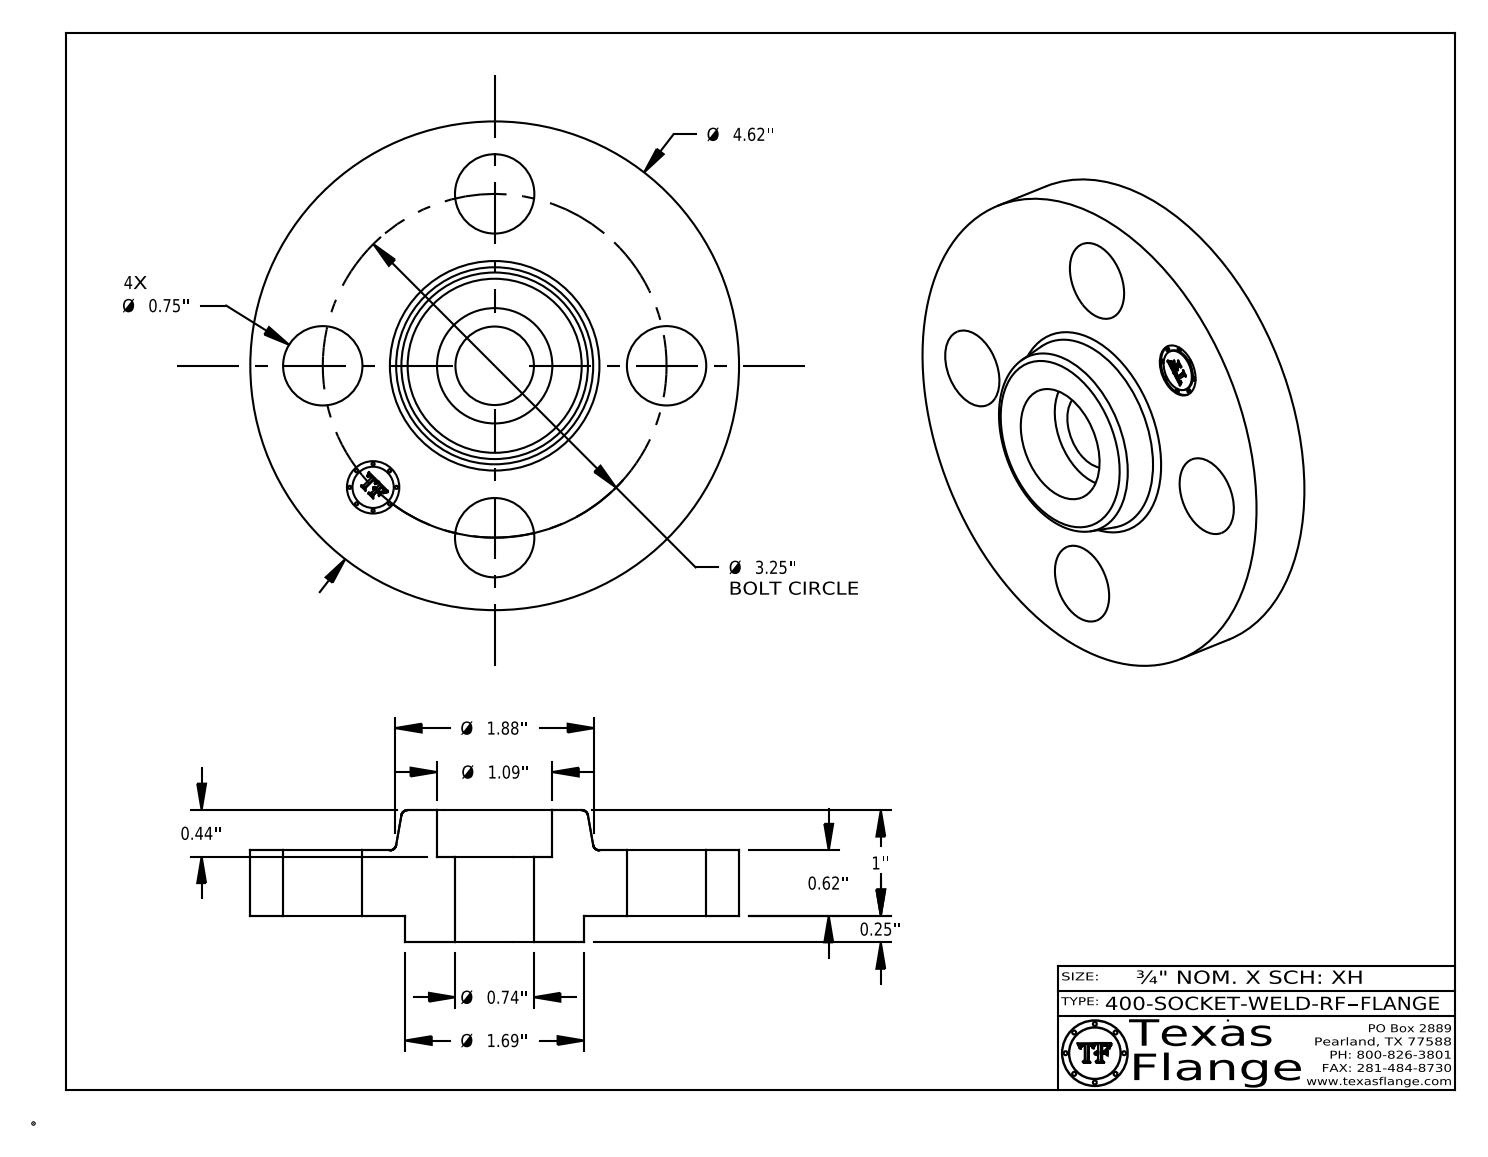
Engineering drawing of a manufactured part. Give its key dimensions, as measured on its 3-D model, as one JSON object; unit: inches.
{"part_name": "400-SOCKET-WELD-RF", "step_written_by": "CATIA V5 STEP AP214 (AUTOMOTIVE_DESIGN)", "units": "inches", "bodies": {"solids": 1, "faces": 412, "planar": 370, "cylindrical": 36, "other": 6}, "overall_size": [4.62, 4.62, 1.25], "volume_in3": 10.08, "surface_area_in2": 50.41, "round_holes": [[0.75, 4], [0.495, 1], [0.742, 1], [1.09, 1]], "round_bosses_or_shafts": [[0.03, 8], [4.62, 1], [1.69, 1], [0.39, 1]], "face_to_face_distances": [0.62, 0.25, 0.87, 1.25, 1, 0.38, 0.81, 0.56, 0.06, 0.44], "hole_center_spacings": [1.625, 2.298, 1.244, 3.003, 3.25]}
